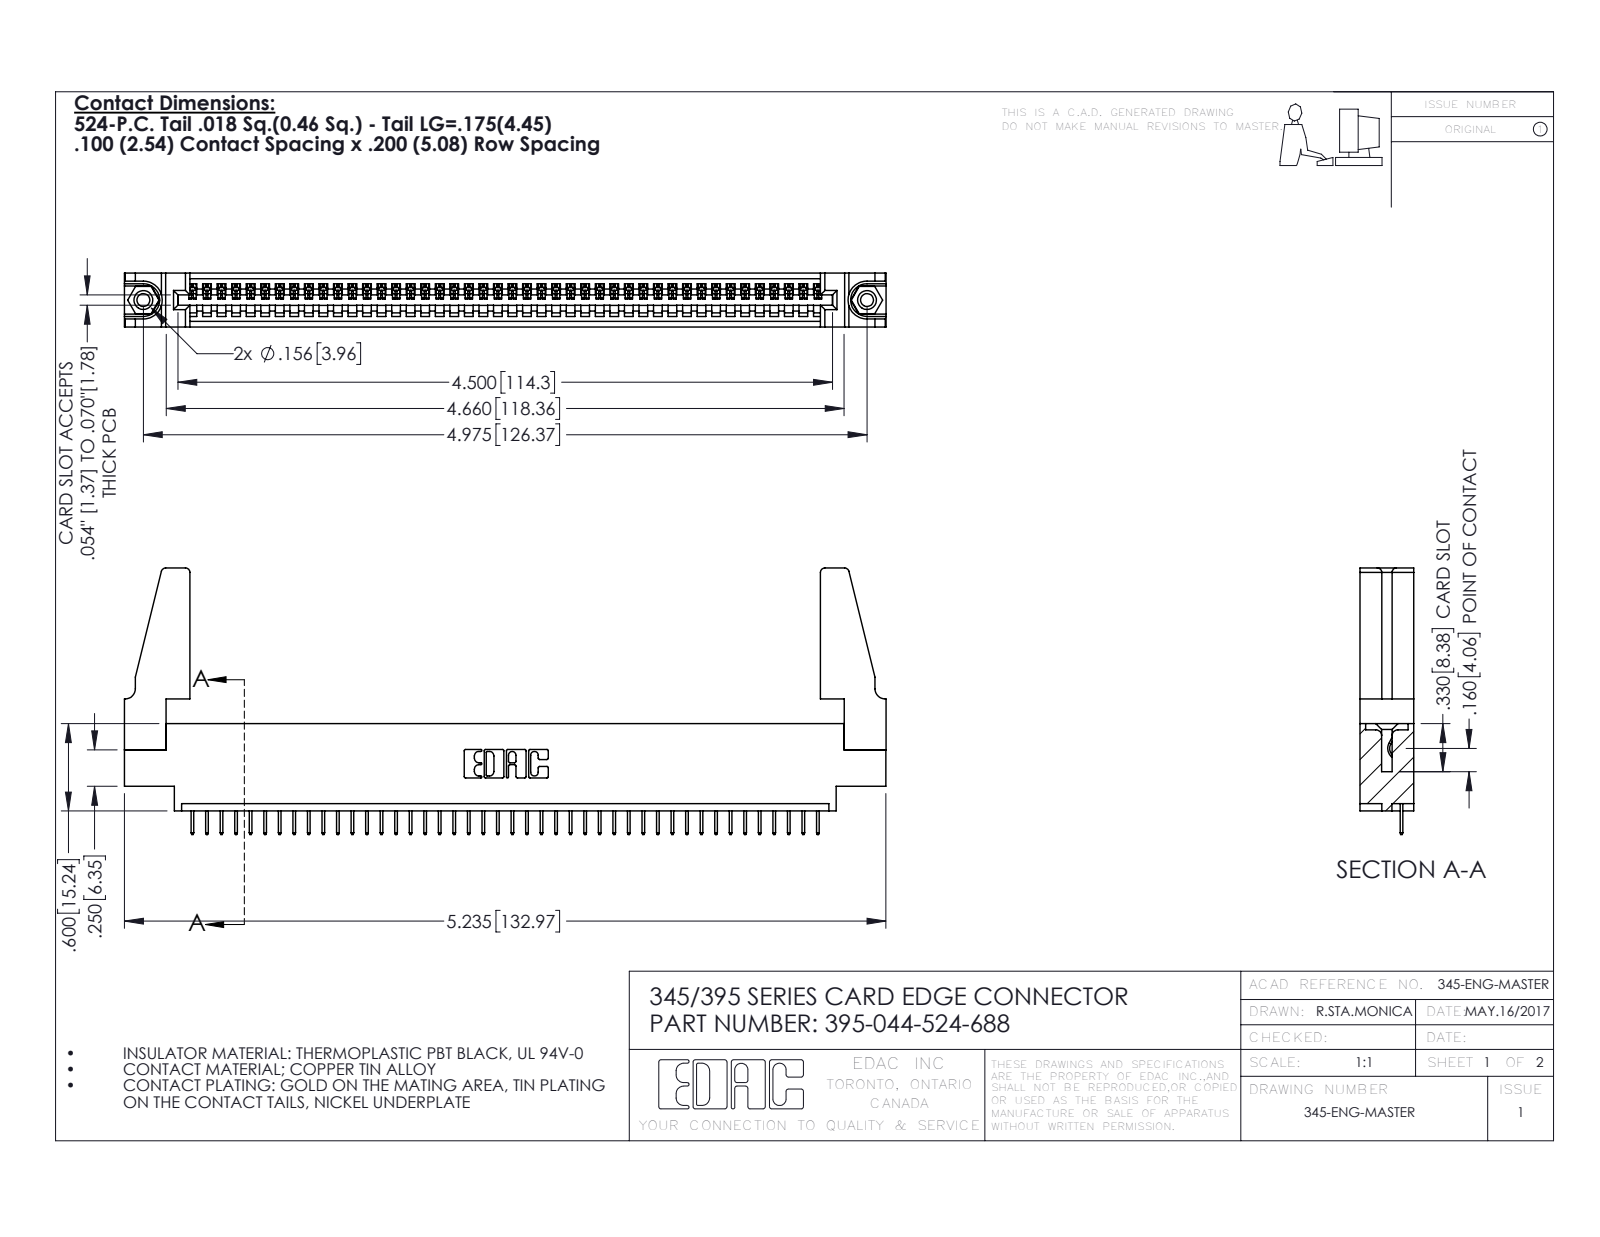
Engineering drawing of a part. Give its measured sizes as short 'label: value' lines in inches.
name: 345-250-001_345-250-001-102; 345 Part_0.170 Offset - 0.156 Dia-TH; 395-044-524-688; 345-220-078_345-220-088 (+1 more)
written by: SolidWorks 2016 (CONFIG_CONTROL_DESIGN)
unit: in
bodies: 49 solids, 2982 faces (2180 planar, 786 cylindrical, 16 other)
size: 5.236 × 1.832 × 0.37
volume: 0.953 in³; area: 29.69 in²
holes: 2× ⌀0.089, 2× ⌀0.125, 2× ⌀0.156, 1× ⌀0.064
bosses: 2× ⌀0.155
rounds: 88× R0.006, 22× R0.01, 8× R0.03, 6× R0.007, 6× R0.031, 3× R0.026, 2× R0.031, 2× R0.04
face distances: 0.37, 0.072, 0.298, 0.2, 0.098, 0.272, 0.025, 0.225, 0.072, 0.175
hole spacings: 0.27, 4.739, 4.975
